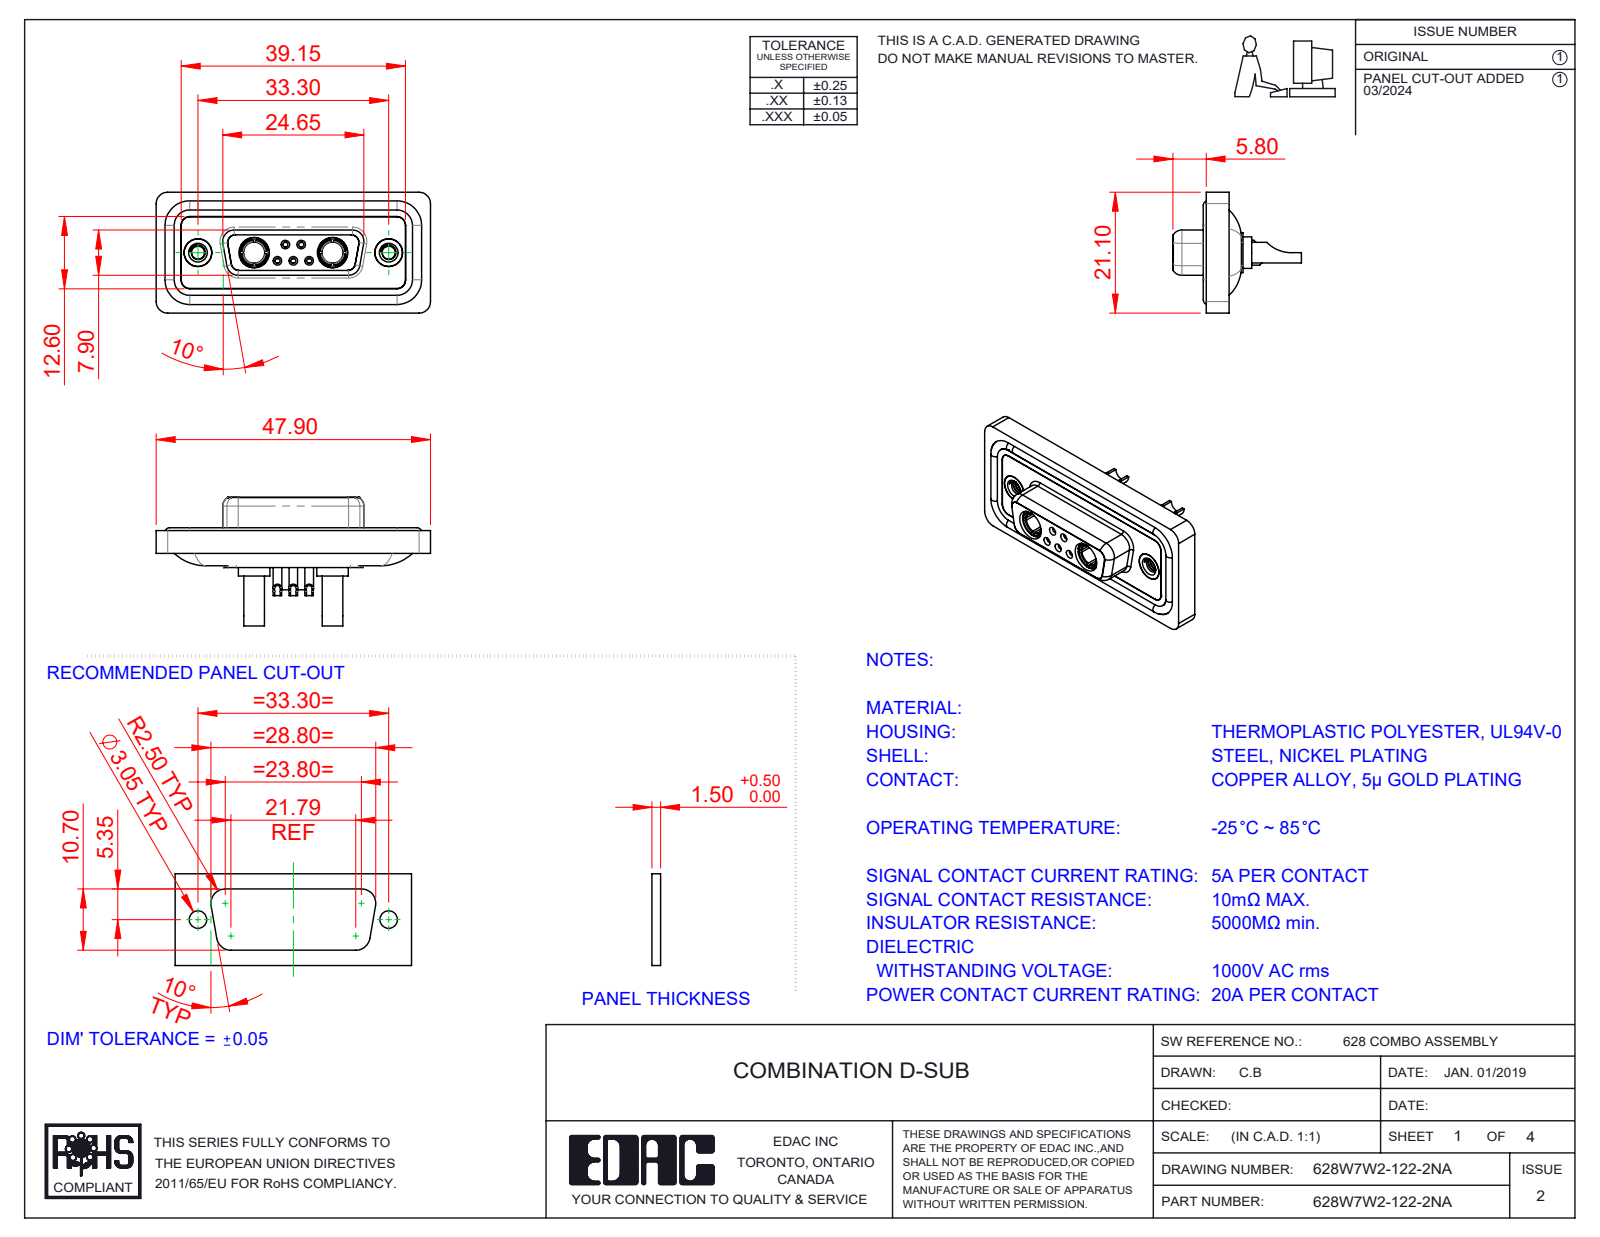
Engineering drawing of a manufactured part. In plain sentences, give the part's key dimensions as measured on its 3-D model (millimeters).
The part is named "Power Socket_20A SC; 628Combo Contact Row 2_22; 628Combo Threaded Rivet_A; 628Combo Contact Row 1_22 (+5 more)". Its 3-D file was written by "SolidWorks 2023 (CONFIG_CONTROL_DESIGN)". It is 16 solids with 819 faces: 254 planar, 347 cylindrical and 218 other. Overall it measures 47.9 by 22.45 by 21.1 millimeters. Its volume is 6 115 cubic millimeters and its surface area 10 102 square millimeters. Round holes: 5 of diameter 0.9, 5 of diameter 1, 5 of diameter 1.1, 5 of diameter 1.5, 5 of diameter 2, 4 of diameter 4.85, 3 of diameter 1.6, 2 of diameter 1.7, 2 of diameter 2.26, 2 of diameter 2.7, 2 of diameter 3.7, 2 of diameter 4. Round bosses or shafts: 6 of diameter 1.6, 5 of diameter 2.2, 2 of diameter 5.5, 2 of diameter 5.2, 2 of diameter 4.96, 2 of diameter 4.95, 2 of diameter 4.8, 2 of diameter 4.75. Partial cylindrical surfaces (rounded edges, fillets, slot ends): 22 of radius 1.5, 20 of radius 2, 12 of radius 1.35, 8 of radius 1.6, 6 of radius 1, 4 of radius 0.25, 4 of radius 0.5, 4 of radius 0.6. The main face-to-face distances are 0.4, 1.8, 1.6, 0.5, 2.9, 1.1, 7.45, 5.65, 6.6, 7.05. The hole center spacings are 3.16, 2.77, 9.8, 23.5, 4.31, 4.33, 5.03, 5.04.
